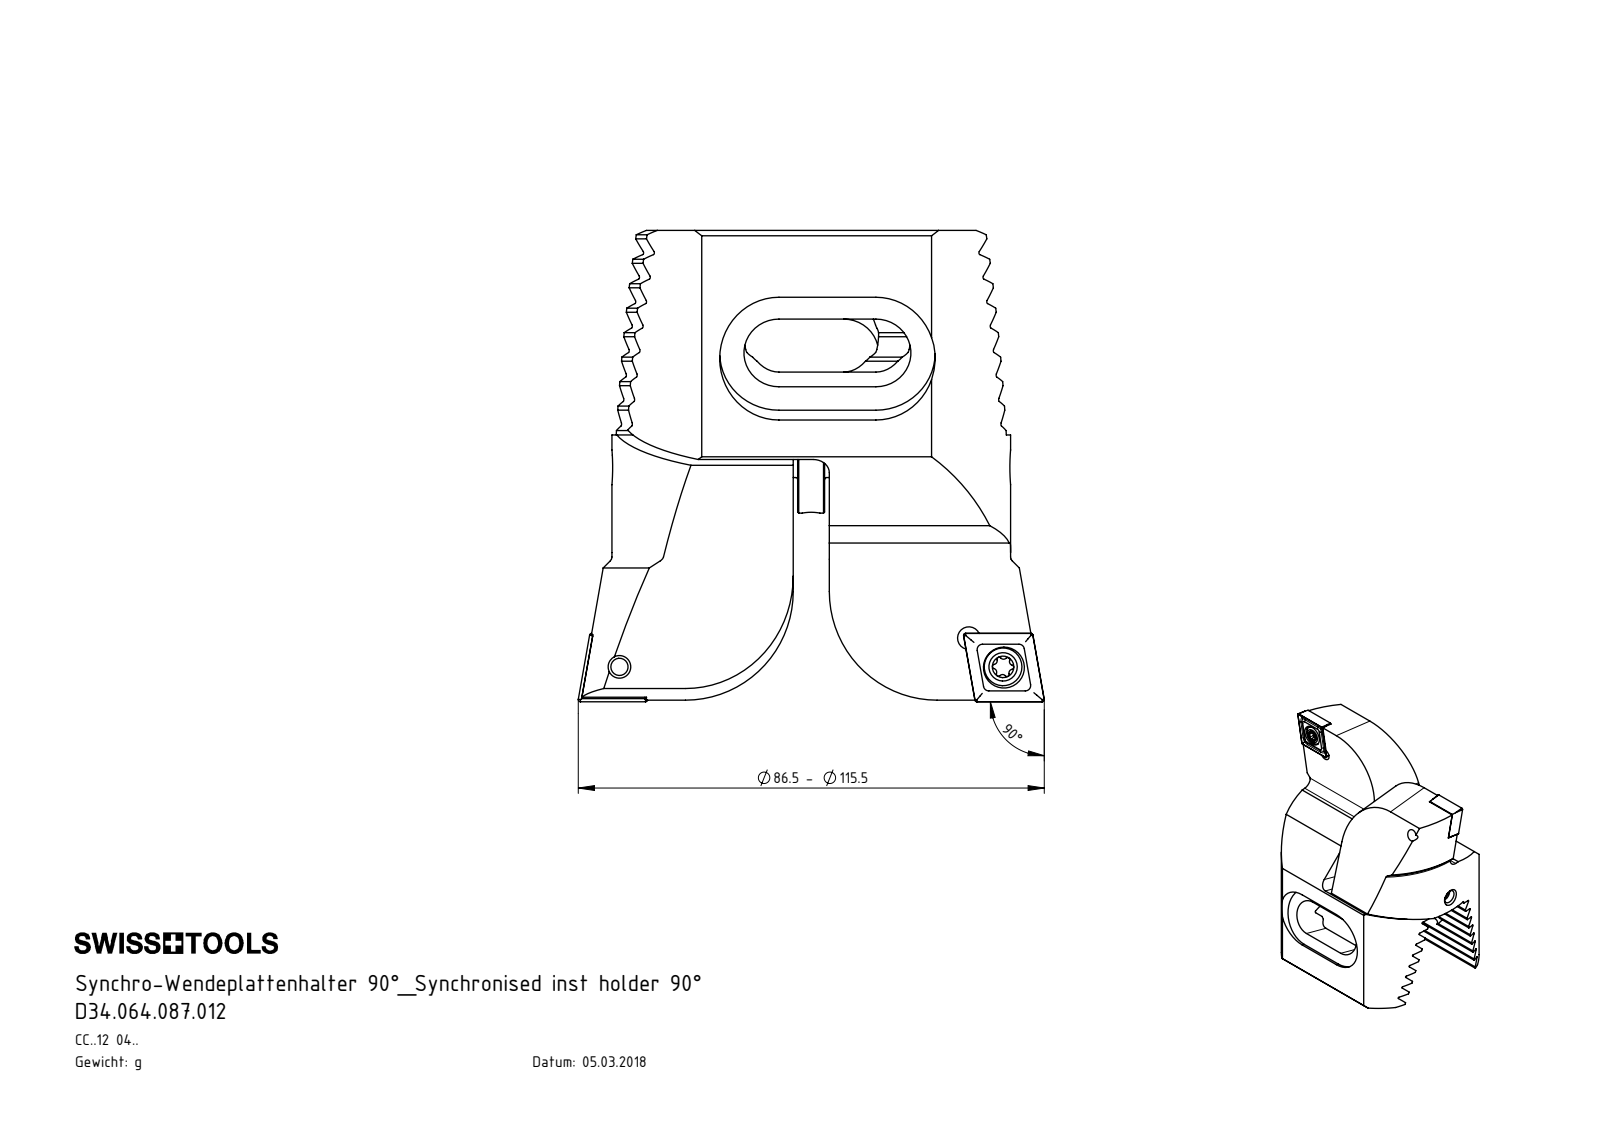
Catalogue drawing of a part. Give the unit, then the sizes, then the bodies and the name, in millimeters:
Units: millimetres
Overall size (bounding box): 87.45 × 86.5 × 58
Round holes (diameter × count): ⌀4.2 ×4, ⌀3.3 ×3, ⌀1 ×2, ⌀5.5 ×2, ⌀7.6 ×2, ⌀5 ×1
Round bosses / shafts (diameter × count): ⌀4 ×3, ⌀7 ×2, ⌀5 ×2, ⌀17 ×1, ⌀6 ×1, ⌀3.8 ×1
Partial cylindrical surfaces — rounded edges, fillets, slot ends (radius × count): R0.34 ×16, R0.39 ×12, R0.69 ×8, R1 ×8, R0.69 ×4, R3 ×4, R6.5 ×4, R11 ×4
Main face-to-face distances: 4.07, 8.14, 12.21, 16.28, 28.7, 29.3, 0.91, 24.43, 20.36, 58
Hole centre spacings: 8.3, 8.5, 15, 65.08, 65.24, 71.37, 28.98, 58.5
Volume: 146 963 mm³ · Surface area: 39 210 mm²
Bodies: 11 solids, 499 faces (199 planar, 160 cylindrical, 140 other)
Part name (STEP PRODUCT): D34.064.087.012; Z72-ER3.000.068; ISO 4026 - M4 x 5; Z42-ER3.002.005_A (+4 more)
STEP written by: SolidWorks 2017 (CONFIG_CONTROL_DESIGN)
